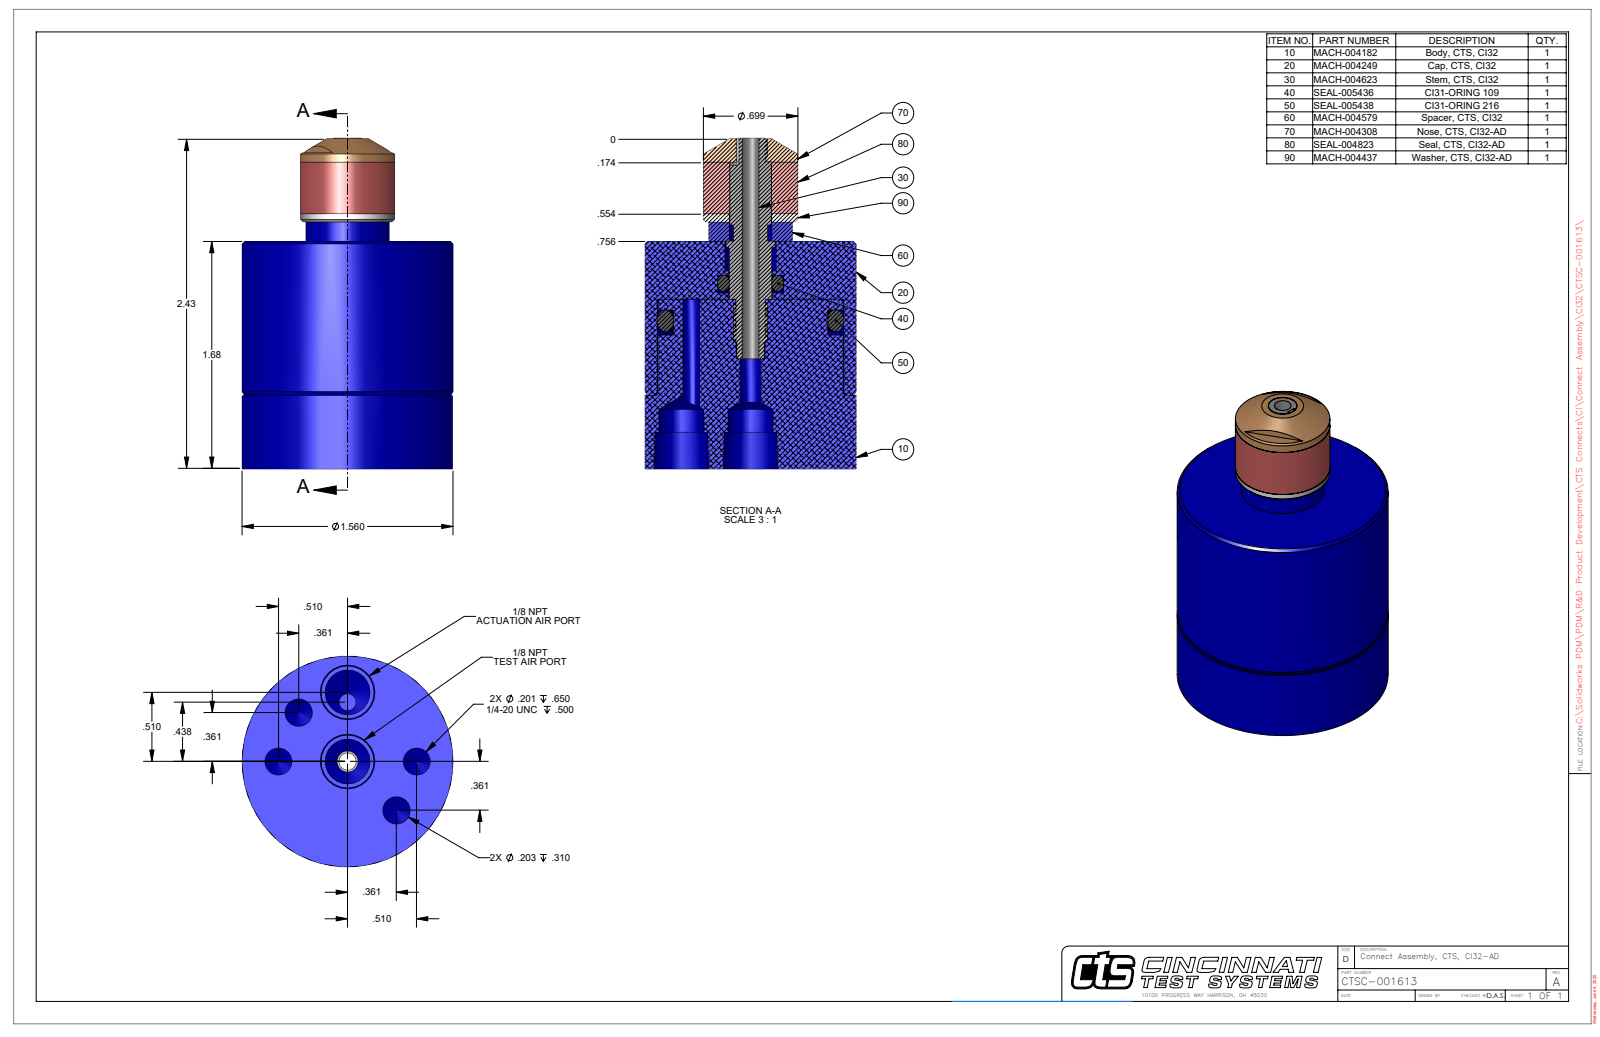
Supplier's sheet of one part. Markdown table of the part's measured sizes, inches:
| quantity | value |
| --- | --- |
| part name | CTSC-001613 |
| STEP written by | SolidWorks 2023 (AUTOMOTIVE_DESIGN) |
| units | inches |
| bodies | 1 solid, 102 faces (29 planar, 39 cylindrical, 34 other) |
| overall size | 2.437 × 1.56 × 1.56 |
| volume | 3.256 in³ |
| surface area | 19.75 in² |
| round holes (diameter × count) | 0.125 × 2, 0.201 × 2, 0.203 × 2, 0.332 × 2, 0.156 × 1, 0.314 × 1, 0.38 × 1, 1.377 × 1 |
| round bosses / shafts (diameter × count) | 1.56 × 1, 1.365 × 1, 0.699 × 1, 0.618 × 1, 0.357 × 1, 0.31 × 1 |
| partial cylindrical surfaces (radius × count) | 0.106 × 1 |
| main face-to-face distances | 1.677, 0.542, 1.135, 0.273, 0.269, 1.404, 2.329, 2.056, 1.787, 0.652 |
| hole center spacings | 0.51, 0.39, 0.942, 0.672, 0.721, 0.072, 0.369, 0.437 |
